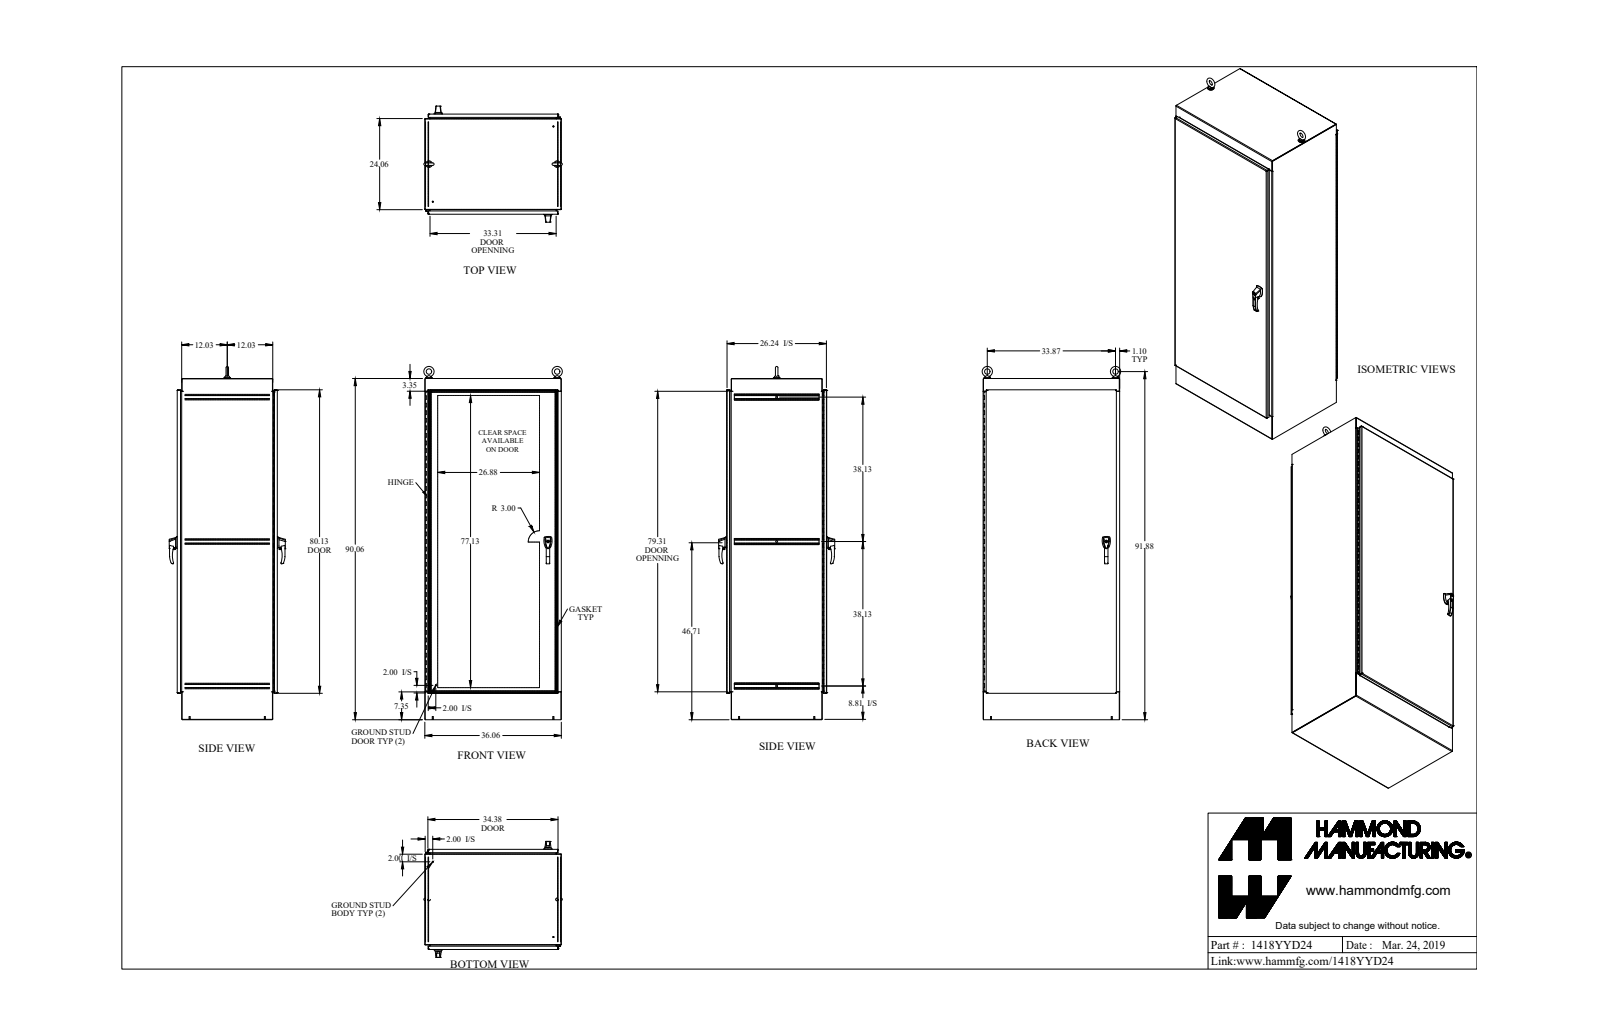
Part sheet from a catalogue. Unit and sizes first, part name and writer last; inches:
Units: inches
Overall size (bounding box): 93.713 × 37.119 × 30.664
Round holes (diameter × count): ⌀0.304 ×28, ⌀0.25 ×4, ⌀0.257 ×4, ⌀0.28 ×4, ⌀0.281 ×4, ⌀0.313 ×4, ⌀0.39 ×4, ⌀0.413 ×4, ⌀0.5 ×3, ⌀0.11 ×2, ⌀0.173 ×2, ⌀0.233 ×2
Round bosses / shafts (diameter × count): ⌀0.281 ×8, ⌀1 ×4, ⌀0.75 ×4, ⌀0.63 ×4, ⌀0.625 ×4, ⌀0.44 ×4, ⌀0.37 ×4, ⌀0.25 ×4
Partial cylindrical surfaces — rounded edges, fillets, slot ends (radius × count): R0.125 ×44, R0.043 ×42, R0.138 ×36, R0.018 ×32, R0.048 ×24, R0.143 ×24, R0.06 ×16, R0.318 ×13
Main face-to-face distances: 0.095, 26.339, 35.965, 26.244, 26.434, 35.87, 1.187, 25.152, 36.06, 89.965
Hole centre spacings: 6, 12, 18, 24, 30, 34.853, 36, 36.369
Volume: 1 482 in³ · Surface area: 31 488 in²
Bodies: 83 solids, 4831 faces (2044 planar, 2521 cylindrical, 266 other)
Part name (STEP PRODUCT): 1418YYD24_Default
STEP written by: SolidWorks 2019 (CONFIG_CONTROL_DESIGN)
